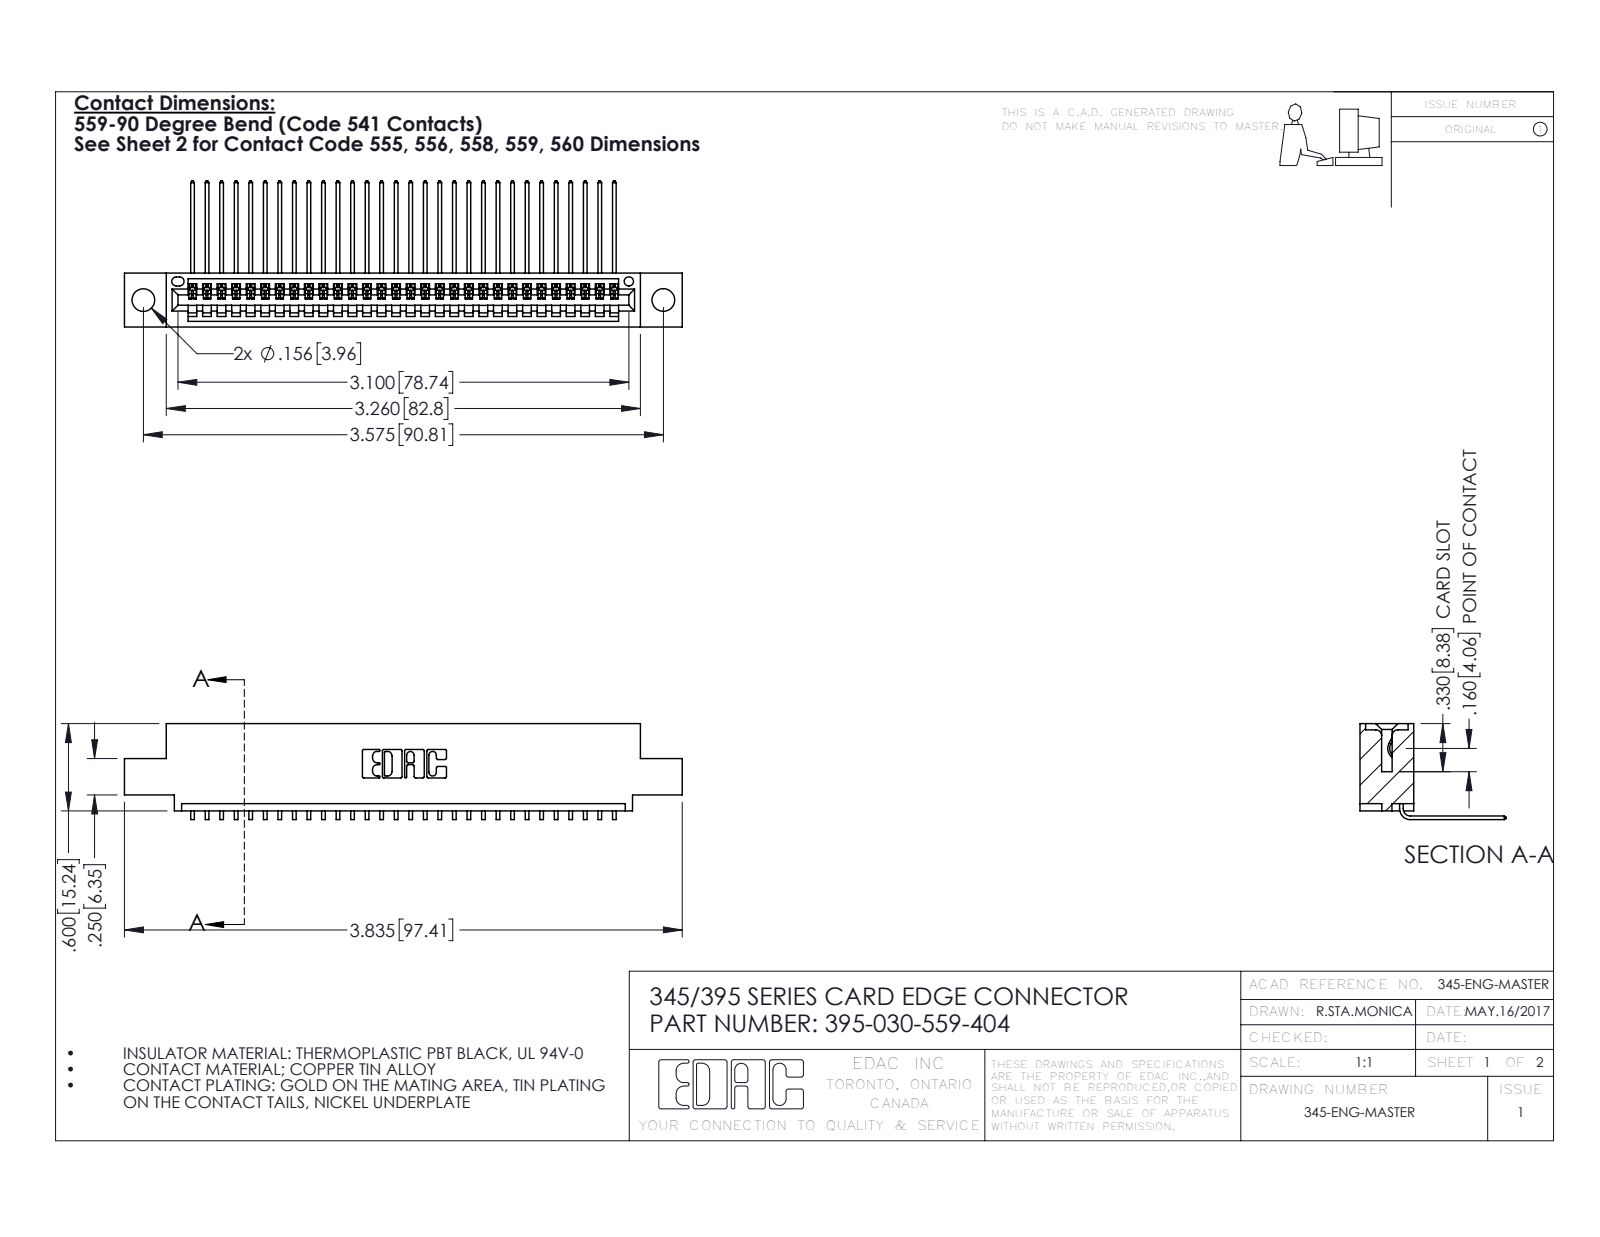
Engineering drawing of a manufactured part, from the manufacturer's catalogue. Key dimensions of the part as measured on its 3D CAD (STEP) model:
Part name (STEP PRODUCT): 345-292-001_558 559 Tail - 1; 345 Part_0.110 Offset - 0.156 Dia-TH; 395-030-559-404
STEP written by: SolidWorks 2016 (CONFIG_CONTROL_DESIGN)
Units: inches
Bodies: 31 solids, 1930 faces (1344 planar, 586 cylindrical, 0 other)
Overall size (bounding box): 3.835 × 1.005 × 0.659
Volume: 0.555 in³ · Surface area: 19.22 in²
Round holes (diameter × count): ⌀0.156 ×2, ⌀0.064 ×1
Partial cylindrical surfaces — rounded edges, fillets, slot ends (radius × count): R0.006 ×60, R0.01 ×22, R0.007 ×6, R0.031 ×6, R0.026 ×3, R0.031 ×2, R0.04 ×2, R0.014 ×1
Main face-to-face distances: 0.072, 0.298, 0.37, 0.2, 0.098, 0.272, 0.025, 0.225, 0.149, 0.072
Hole centre spacings: 0.27, 3.34, 3.575
